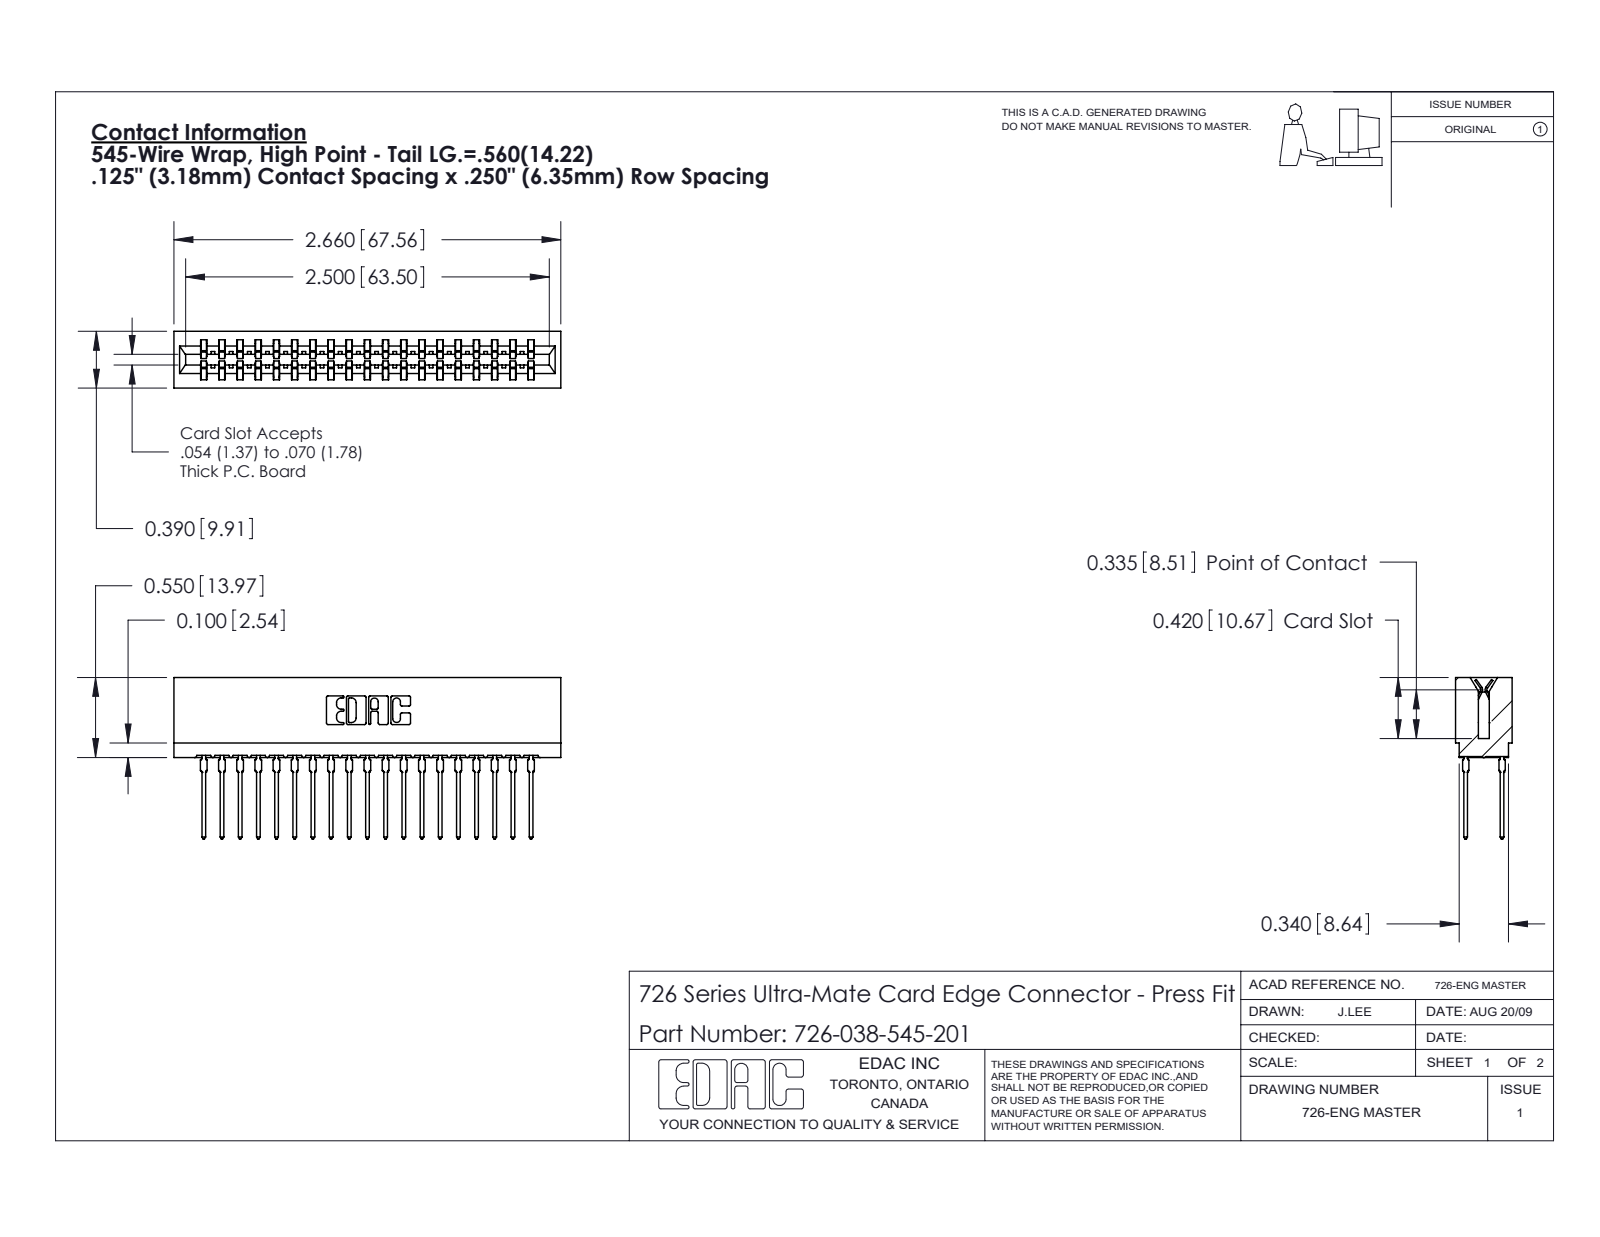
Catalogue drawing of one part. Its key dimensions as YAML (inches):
part_name: "726-038-545-201; 726 Part_.515 Slot Depth - 01; 746-292-001_545"
step_written_by: "SolidWorks 2020 (CONFIG_CONTROL_DESIGN)"
units: inches
bodies: {solids: 39, faces: 3498, planar: 1803, cylindrical: 707, other: 988}
overall_size: [2.66, 1.109, 0.39]
volume: 0.395
surface_area: 17.02
partial_cylinders:
  - {radius: 0.021, count: 76}
  - {radius: 0.01, count: 22}
  - {radius: 0.015, count: 20}
  - {radius: 0.005, count: 8}
  - {radius: 0.011, count: 8}
  - {radius: 0.007, count: 6}
  - {radius: 0.031, count: 6}
  - {radius: 0.026, count: 3}
face_to_face_distances: [0.057, 0.333, 0.25, 0.025, 0.307, 0.39, 0.5, 0.083, 0.275, 0.125]
